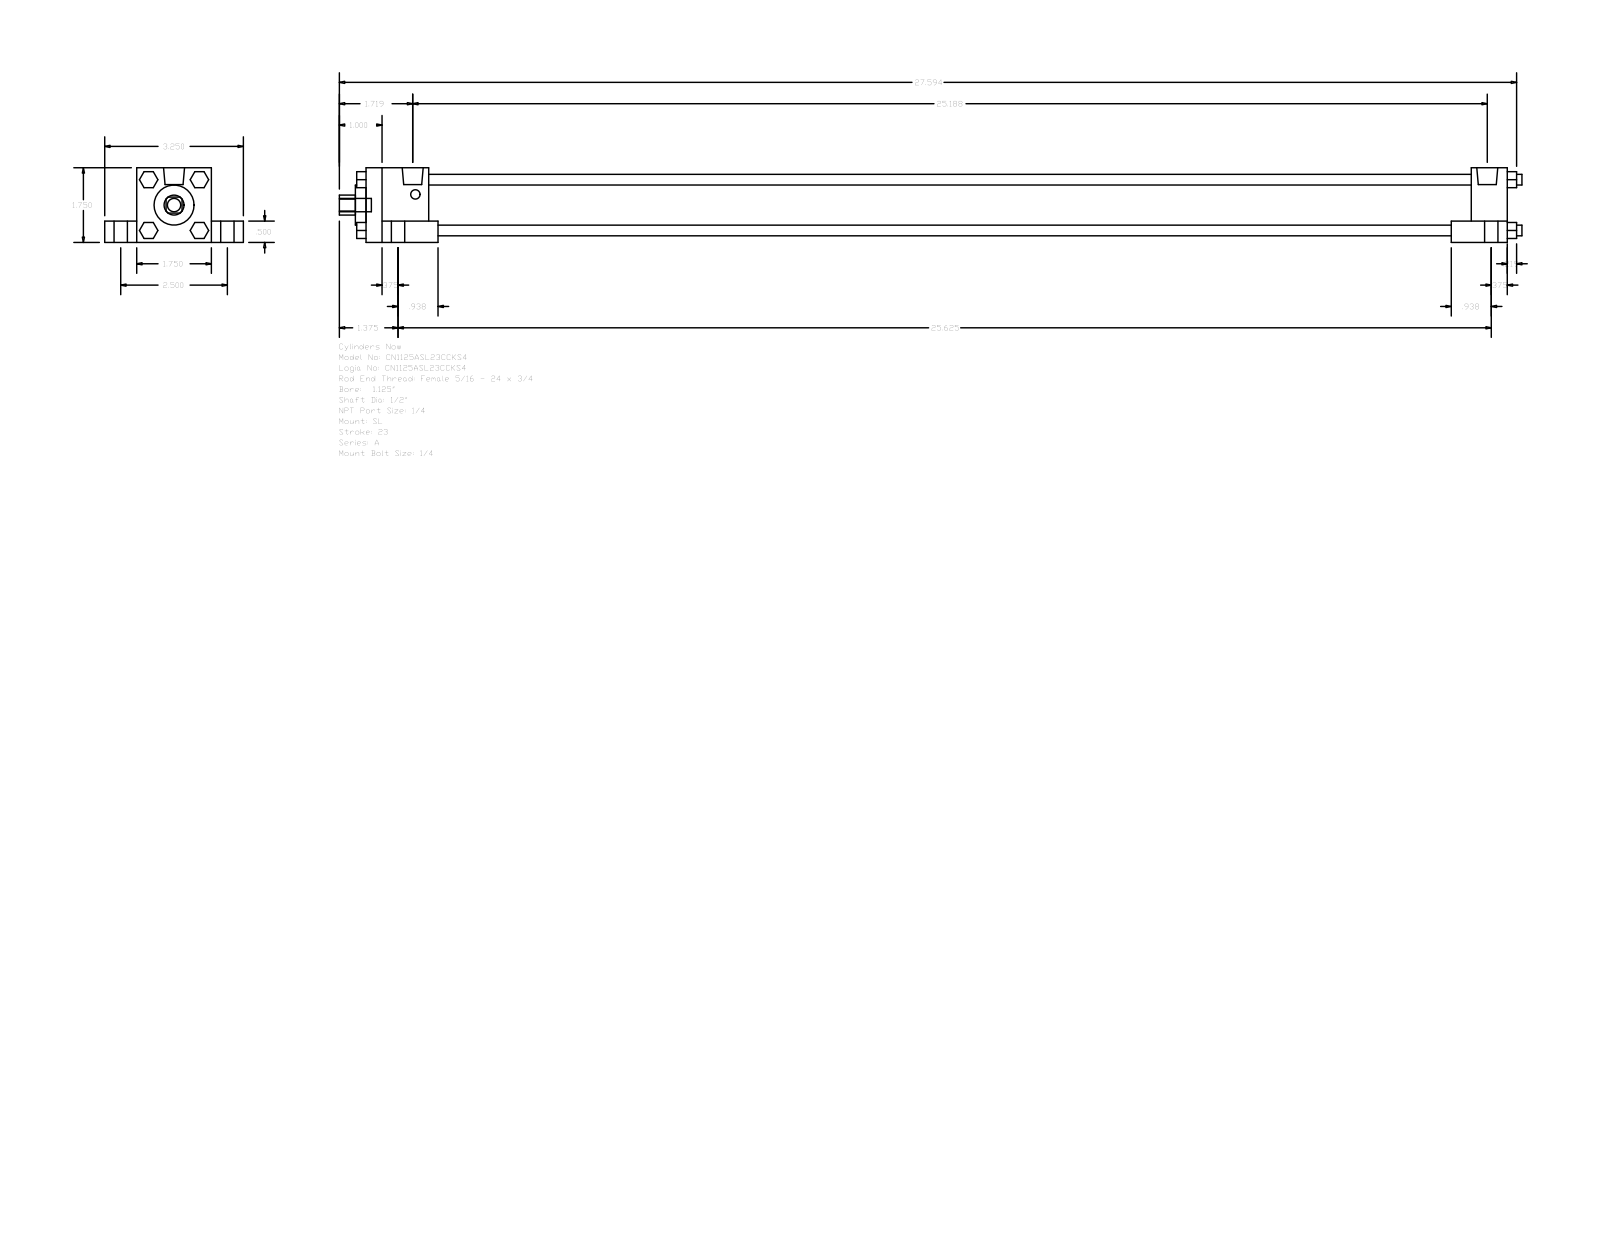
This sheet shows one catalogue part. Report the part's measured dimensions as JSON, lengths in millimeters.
{"part_name": "A_SL__0112_0.5", "step_written_by": "GSSL Pune (CONFIG_CONTROL_DESIGN)", "units": "millimeters", "bodies": {"solids": 0, "faces": 150, "planar": 114, "cylindrical": 36, "other": 0}, "overall_size": [704.06, 82.55, 44.45], "round_holes": [[12.7, 1], [23.81, 1], [31.88, 1]], "round_bosses_or_shafts": [[7.94, 5], [14.29, 4], [6.35, 4], [5.56, 4], [12.49, 2]], "partial_cylinders_radius": [[5.94, 1]], "face_to_face_distances": [44.46, 31.76, 12.7, 19.04, 63.5, 679.45, 658.01, 21.44, 37.3, 620.71]}
